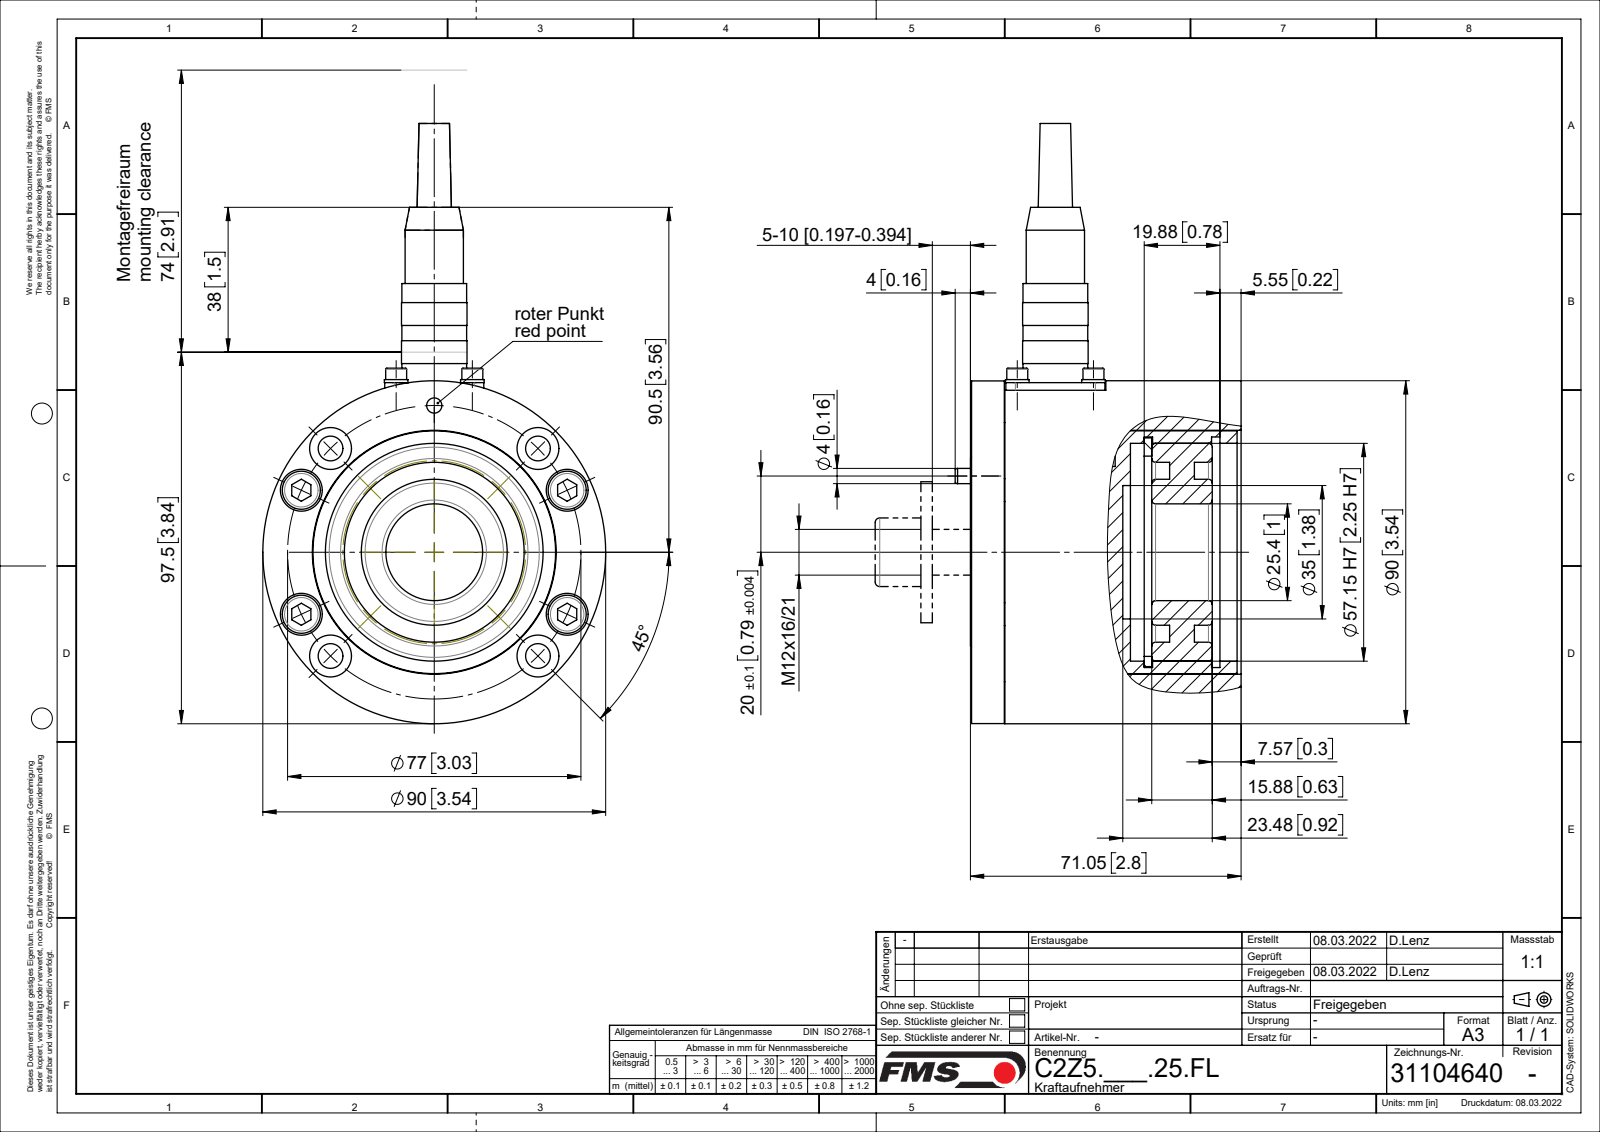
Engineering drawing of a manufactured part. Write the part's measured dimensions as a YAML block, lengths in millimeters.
part_name: "Kabeldose_M14x1_Mini_5pol; Zyl-Schr DIN912_M3x6; Flanschstecker_M14x1_Mini_5pol; Zyl-Schr DIN912_M6x30 (+8 more)"
step_written_by: "SolidWorks 2018 (CONFIG_CONTROL_DESIGN)"
units: millimeters
bodies: {solids: 22, faces: 547, planar: 185, cylindrical: 254, other: 108}
overall_size: [157.5, 96.05, 90]
volume: 316332
surface_area: 122946
round_holes:
  - {diameter: 6.5, count: 8}
  - {diameter: 11, count: 8}
  - {diameter: 2.5, count: 6}
  - {diameter: 3.1, count: 4}
  - {diameter: 3.2, count: 4}
  - {diameter: 5, count: 4}
  - {diameter: 7, count: 4}
  - {diameter: 4, count: 2}
  - {diameter: 3, count: 1}
  - {diameter: 10.2, count: 1}
  - {diameter: 12, count: 1}
  - {diameter: 13, count: 1}
round_bosses_or_shafts:
  - {diameter: 1.5, count: 5}
  - {diameter: 10, count: 4}
  - {diameter: 6.2, count: 4}
  - {diameter: 6, count: 4}
  - {diameter: 5.5, count: 4}
  - {diameter: 3, count: 4}
  - {diameter: 90, count: 1}
  - {diameter: 89.9, count: 1}
partial_cylinders:
  - {radius: 0.1, count: 4}
  - {radius: 2.5, count: 4}
  - {radius: 0.5, count: 2}
  - {radius: 4.16, count: 2}
  - {radius: 5, count: 2}
  - {radius: 23.2, count: 1}
  - {radius: 26.29, count: 1}
face_to_face_distances: [6, 33.05, 32, 2, 38, 8.6, 29.1, 37.7, 2.9, 5.7]
hole_center_spacings: [20, 38.5, 13.37, 14.14, 38.49, 44.16, 54.44, 63.07]
